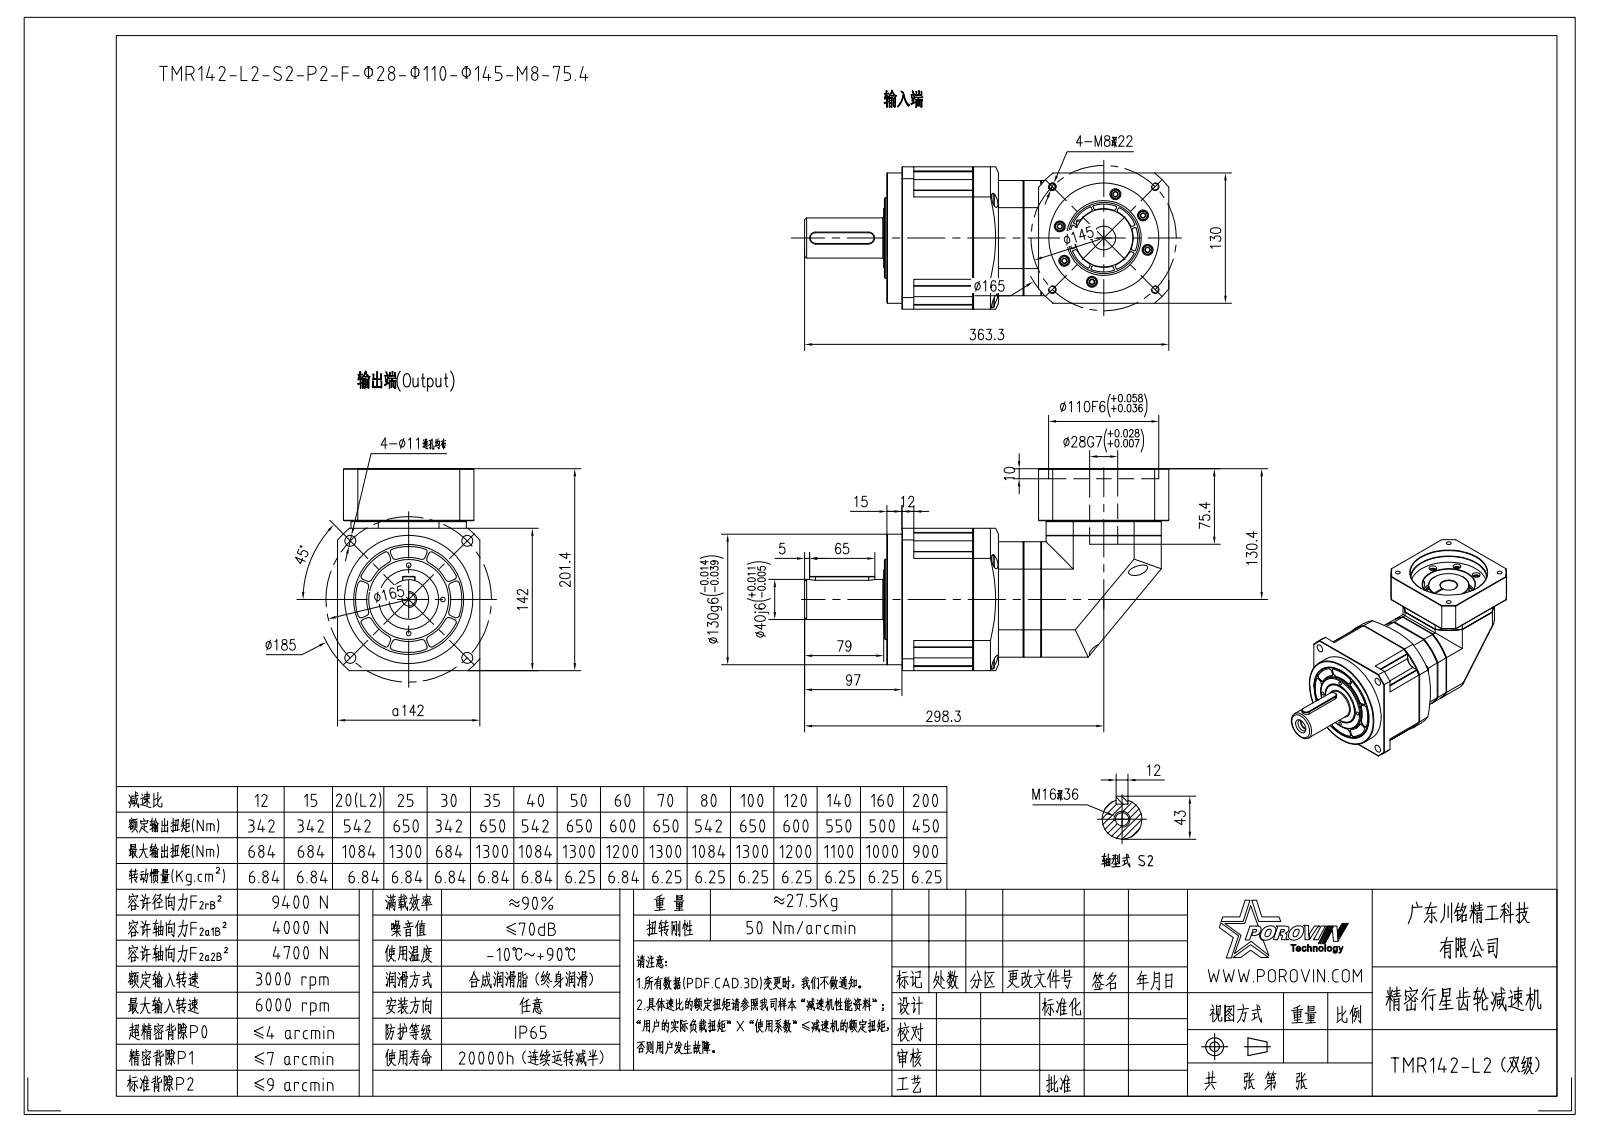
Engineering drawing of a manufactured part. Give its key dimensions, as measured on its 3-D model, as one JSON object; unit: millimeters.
{"part_name": "TMR1150003; HEXAGON_SOCKET_HEAD_CAP_S-20151; SPRING_LOCK_WASHERS--NORMAL_TYP; HEXAGON_SOCKET_HEAD_CAP_S-20104 (+8 more)", "step_written_by": "CREO PARAMETRIC BY PTC INC, 2020053 (CONFIG_CONTROL_DESIGN)", "units": "millimeters", "bodies": {"solids": 47, "faces": 1467, "planar": 614, "cylindrical": 572, "other": 281}, "overall_size": [363.3, 201.4, 142], "volume_mm3": 4277000, "surface_area_mm2": 442374, "round_holes": [[6.68, 16], [11, 16], [5, 13], [6.8, 11], [6.5, 10], [6.6, 6], [14, 5], [9, 4], [10.5, 4], [8.5, 1], [13.6, 1], [17, 1]], "round_bosses_or_shafts": [[10, 16], [9.88, 16], [6, 16], [13, 5], [8, 5], [130, 1], [99, 1], [80, 1]], "partial_cylinders_radius": [[1, 40], [2, 32], [10.5, 4], [6, 2], [65, 2], [5, 1], [6.75, 1], [42.5, 1]], "face_to_face_distances": [13.5, 128.5, 50.3, 18, 7.5, 68.3, 68.1, 17.8, 142, 122.5], "hole_center_spacings": [45.25, 111.28, 12.31, 21.17, 47.5, 51.41, 91.96, 110.07]}
